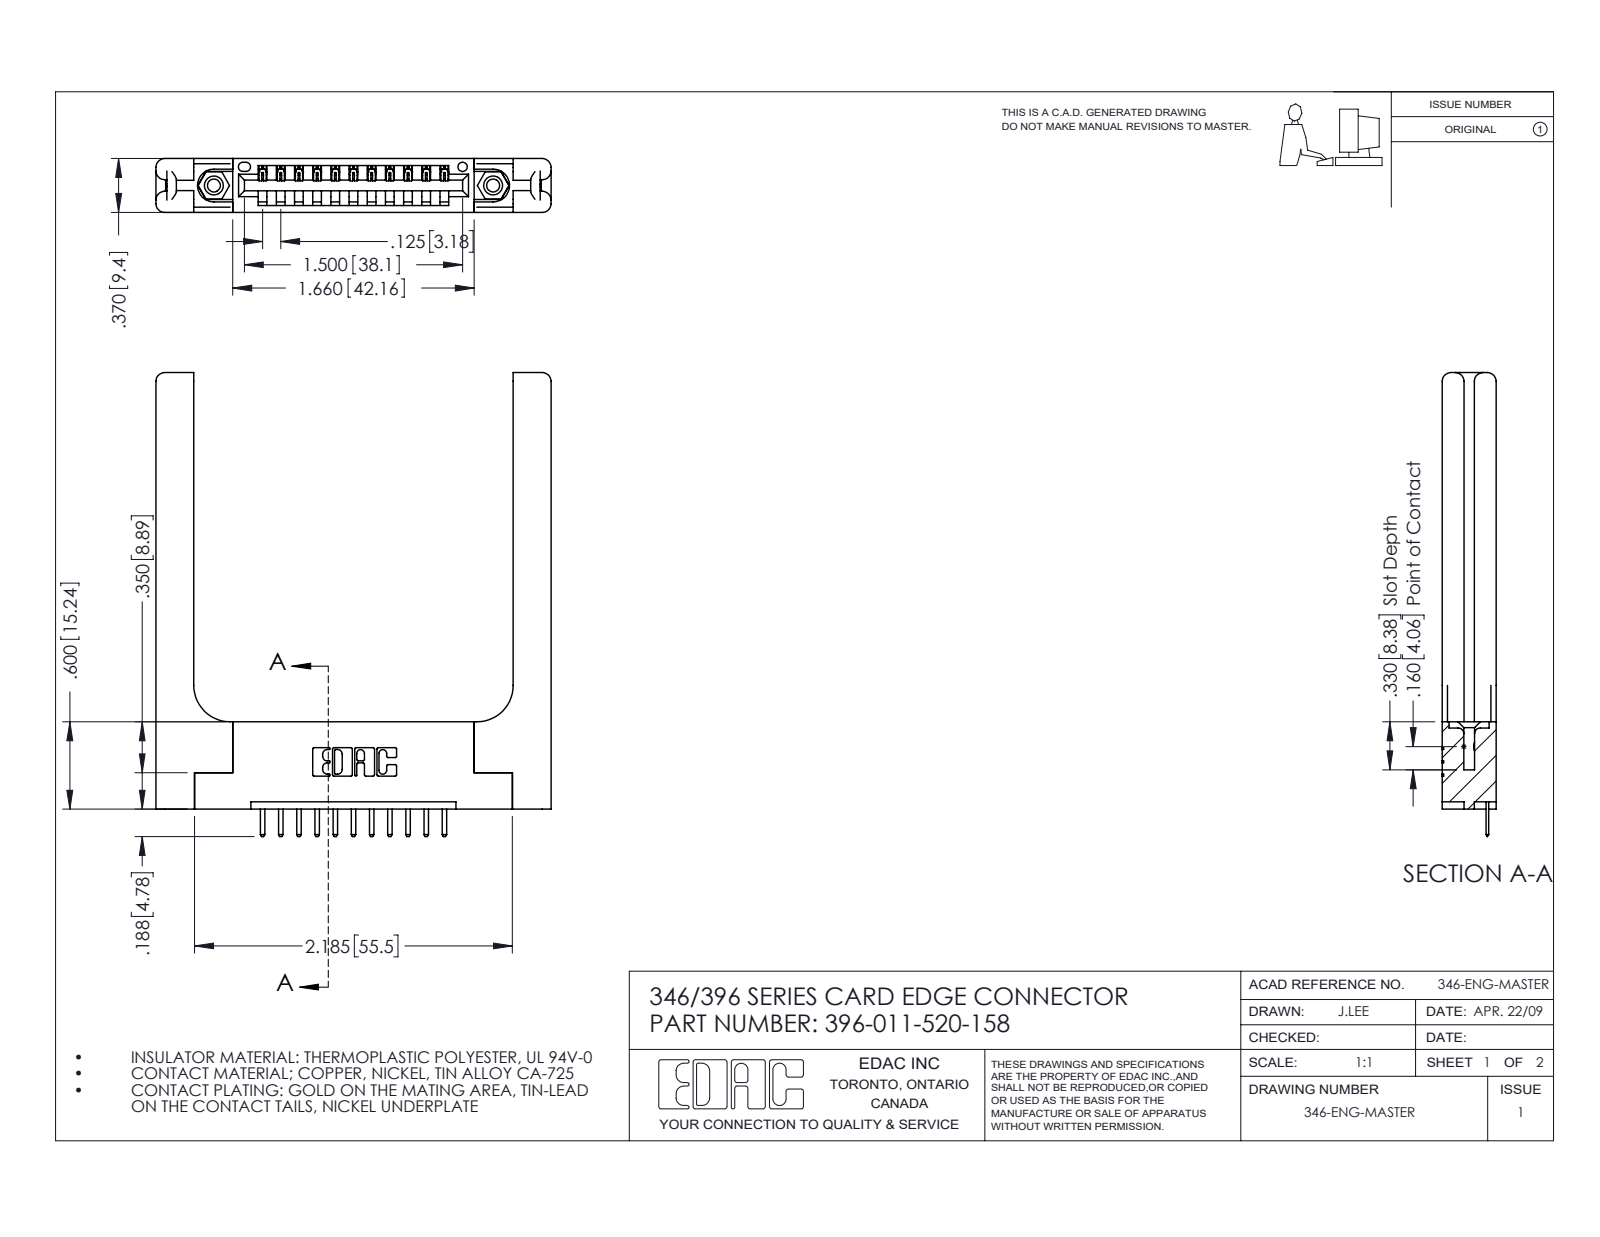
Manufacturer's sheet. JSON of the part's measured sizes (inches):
{"part_name": "396-011-520-158; 346-220-058_345-220-058; 345-292-001_345-293-120; 345-250-001_345-250-001-102 (+1 more)", "step_written_by": "SolidWorks 2016 (CONFIG_CONTROL_DESIGN)", "units": "inches", "bodies": {"solids": 16, "faces": 1060, "planar": 686, "cylindrical": 314, "other": 60}, "overall_size": [3.188, 2.716, 0.37], "volume_in3": 0.847, "surface_area_in2": 19.65, "round_holes": [[0.089, 2], [0.125, 2], [0.156, 2], [0.064, 1]], "round_bosses_or_shafts": [[0.155, 2]], "partial_cylinders_radius": [[0.01, 24], [0.006, 22], [0.01, 22], [0.06, 16], [0.007, 6], [0.031, 6], [0.026, 3], [0.03, 2]], "face_to_face_distances": [0.37, 0.15, 0.072, 0.22, 0.148, 0.25, 0.102, 0.048, 0.322, 0.173], "hole_center_spacings": [0.246, 1.715, 1.92]}
